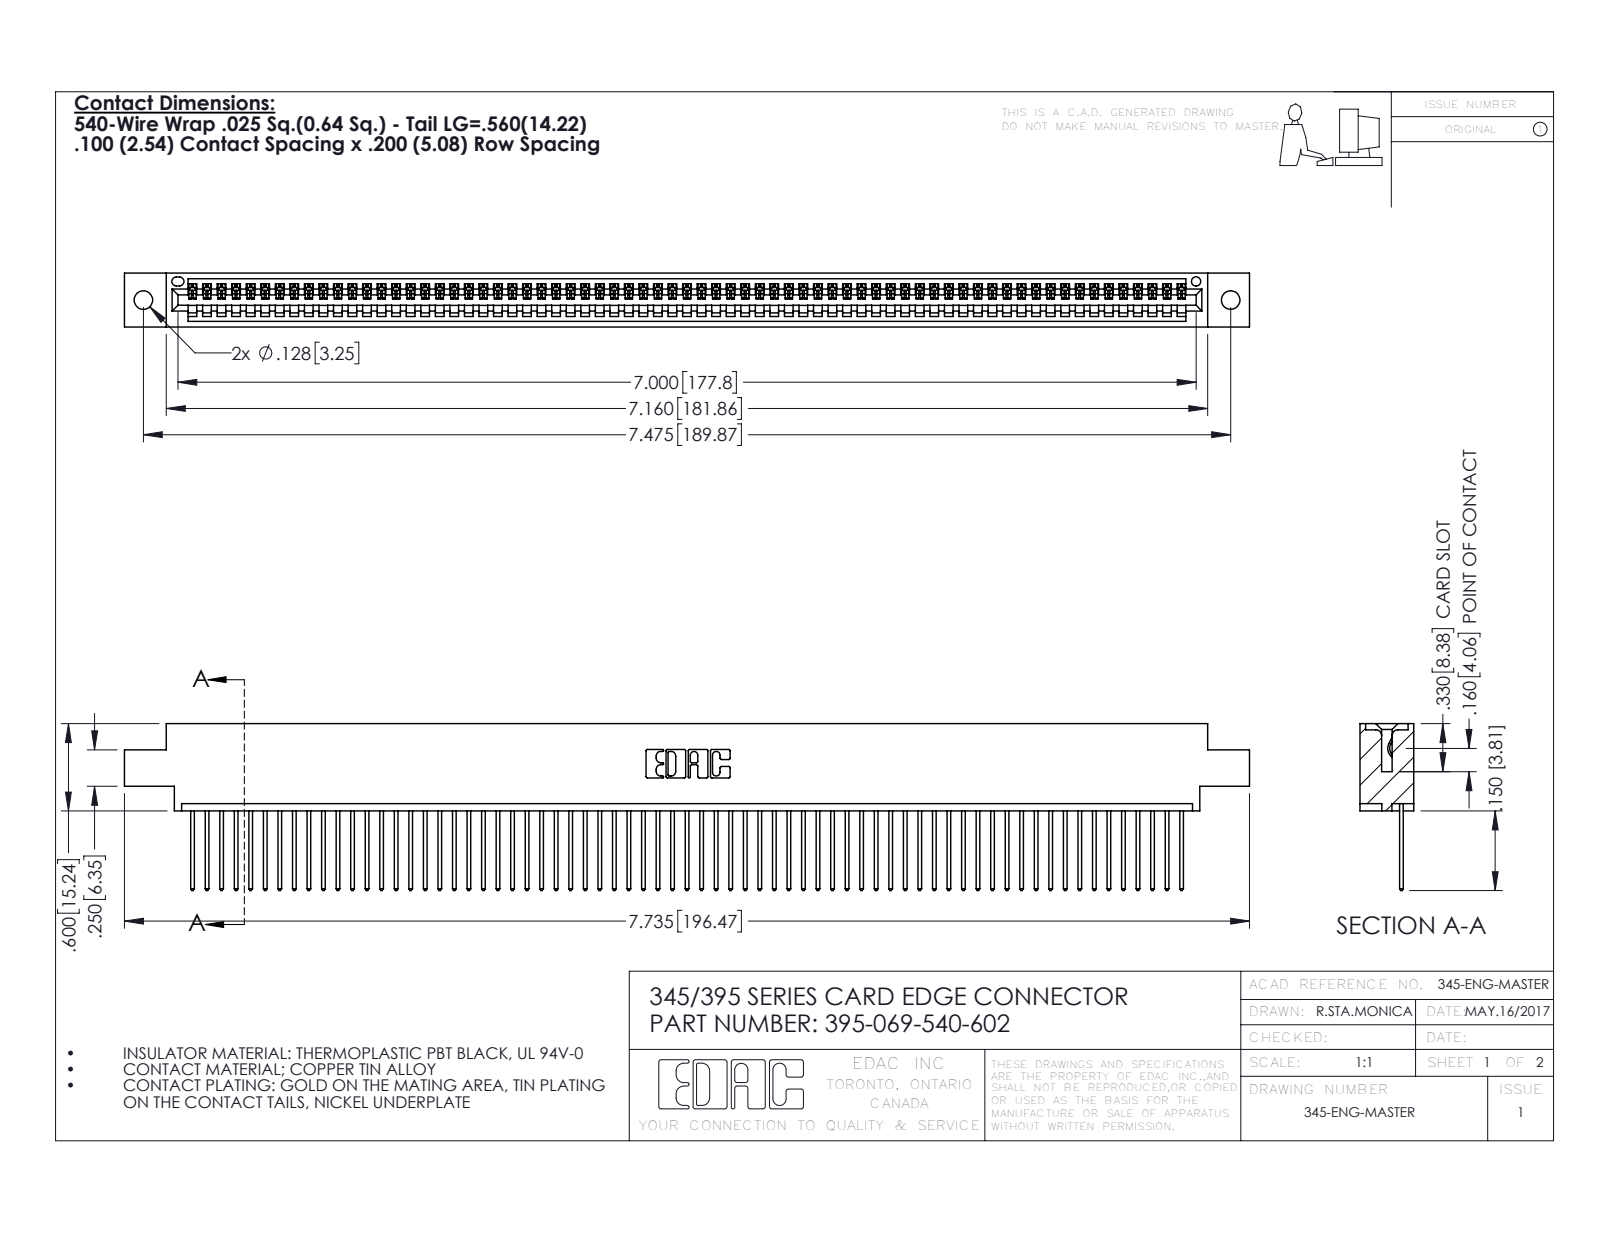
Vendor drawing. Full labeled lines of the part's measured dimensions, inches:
Part name (STEP PRODUCT): 345-292-001_345-293-140; 345 Part_0.170 Offset - 0.128 Dia; 395-069-540-602
STEP written by: SolidWorks 2016 (CONFIG_CONTROL_DESIGN)
Units: inches
Bodies: 70 solids, 4132 faces (2844 planar, 1288 cylindrical, 0 other)
Overall size (bounding box): 7.735 × 1.147 × 0.37
Volume: 1.149 in³ · Surface area: 40.16 in²
Round holes (diameter × count): ⌀0.128 ×2, ⌀0.064 ×1
Partial cylindrical surfaces — rounded edges, fillets, slot ends (radius × count): R0.006 ×138, R0.01 ×138, R0.01 ×22, R0.007 ×6, R0.031 ×6, R0.026 ×3, R0.031 ×2, R0.04 ×2
Main face-to-face distances: 0.072, 0.298, 0.37, 0.098, 0.272, 0.025, 0.2, 0.225, 0.175, 0.149
Hole centre spacings: 0.27, 7.239, 7.475
